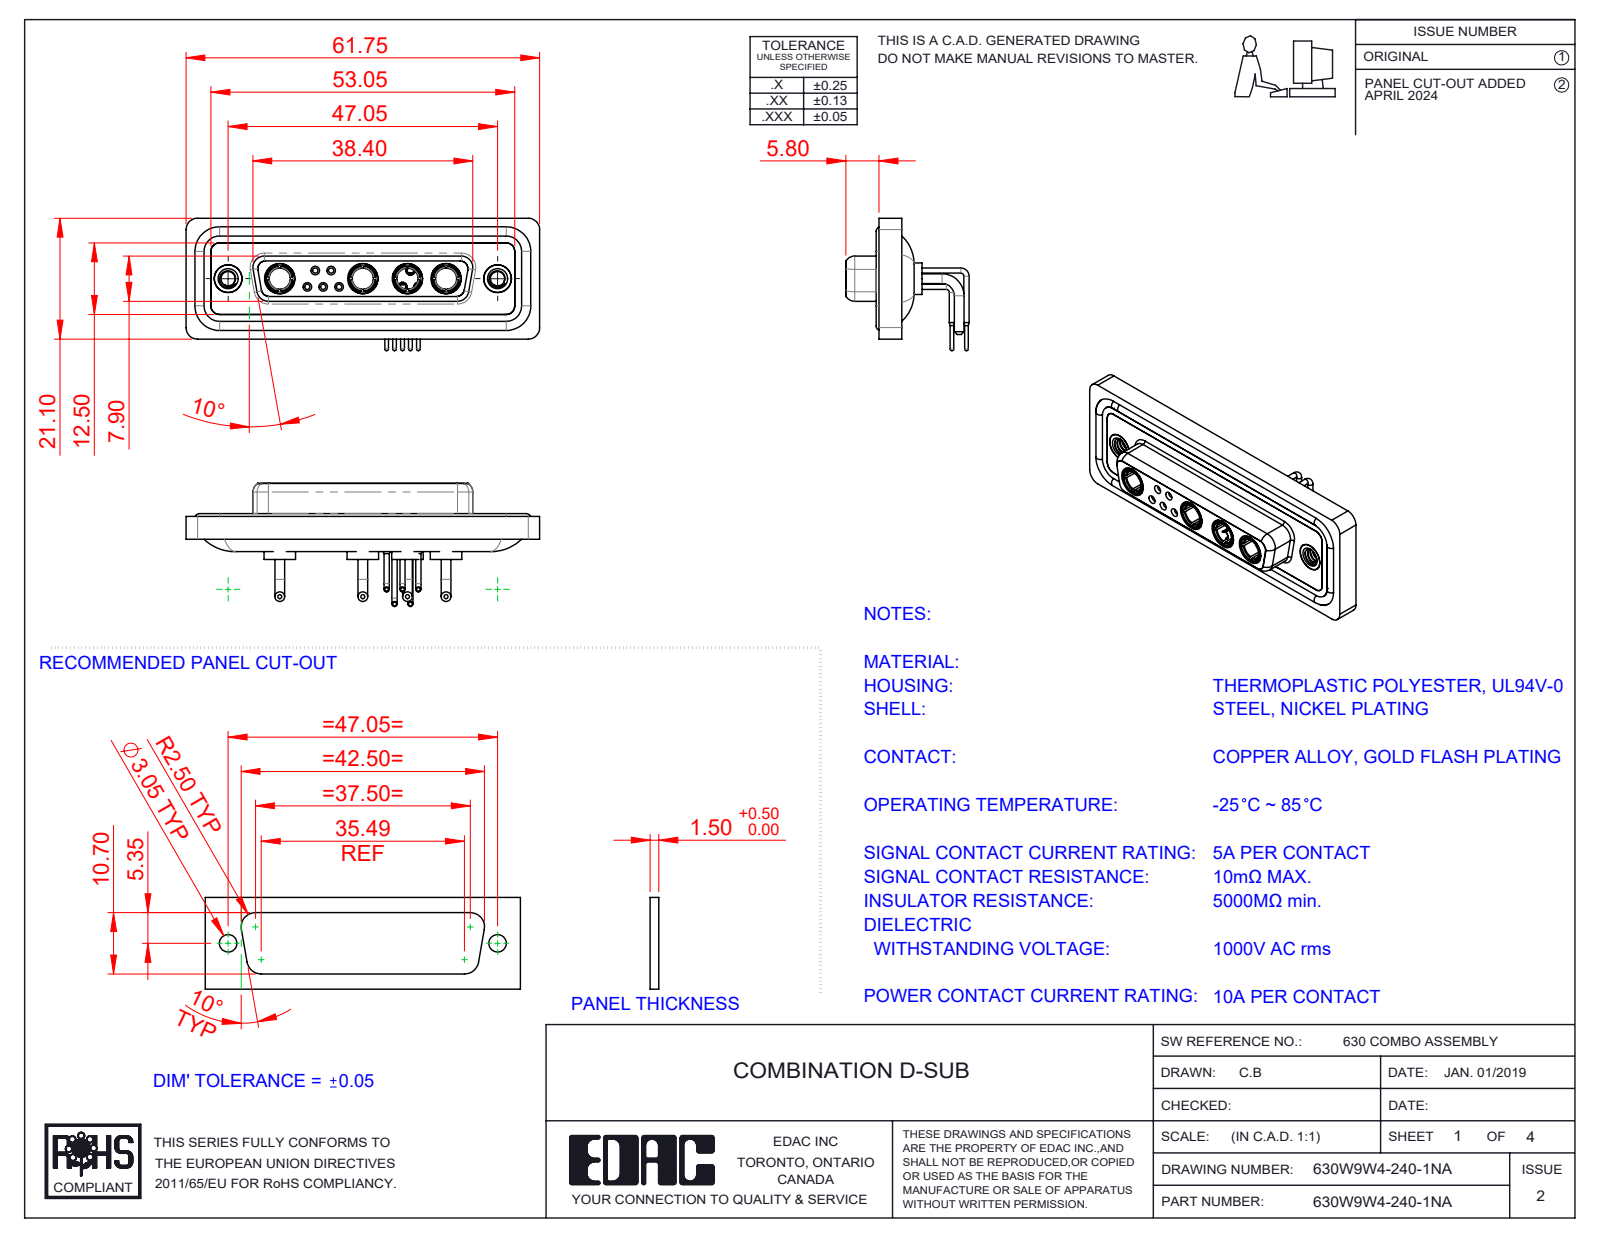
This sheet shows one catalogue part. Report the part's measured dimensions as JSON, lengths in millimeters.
{"part_name": "630Combo Contact Row 1_50 Contacts; Power Socket_10A RA; 630Combo Housing_9W4; 630W9W4-140-1NA (+5 more)", "step_written_by": "SolidWorks 2023 (CONFIG_CONTROL_DESIGN)", "units": "millimeters", "bodies": {"solids": 20, "faces": 957, "planar": 296, "cylindrical": 401, "other": 260}, "overall_size": [61.75, 23.12, 21.53], "volume_mm3": 8213, "surface_area_mm2": 13847, "round_holes": [[4.85, 6], [0.9, 5], [1.1, 5], [1.5, 5], [2, 5], [3.7, 4], [5.3, 4], [1.6, 3], [1.7, 2], [2.5, 2], [4, 2], [4.05, 2]], "round_bosses_or_shafts": [[0.9, 10], [1.6, 9], [1.7, 8], [2, 5], [1.5, 5], [0.65, 5], [5.5, 4], [5.2, 4]], "partial_cylinders_radius": [[1.5, 18], [2, 18], [1.35, 8], [1.6, 8], [0.25, 4], [0.5, 4], [0.6, 4], [0.65, 4]], "face_to_face_distances": [0.4, 1.8, 4.1, 1.1, 1.5, 1.6, 2.5, 3.1, 3.7, 1.4], "hole_center_spacings": [3.16, 2.77, 5.04, 13.85, 11.08, 12.79, 15.5, 5.54]}
